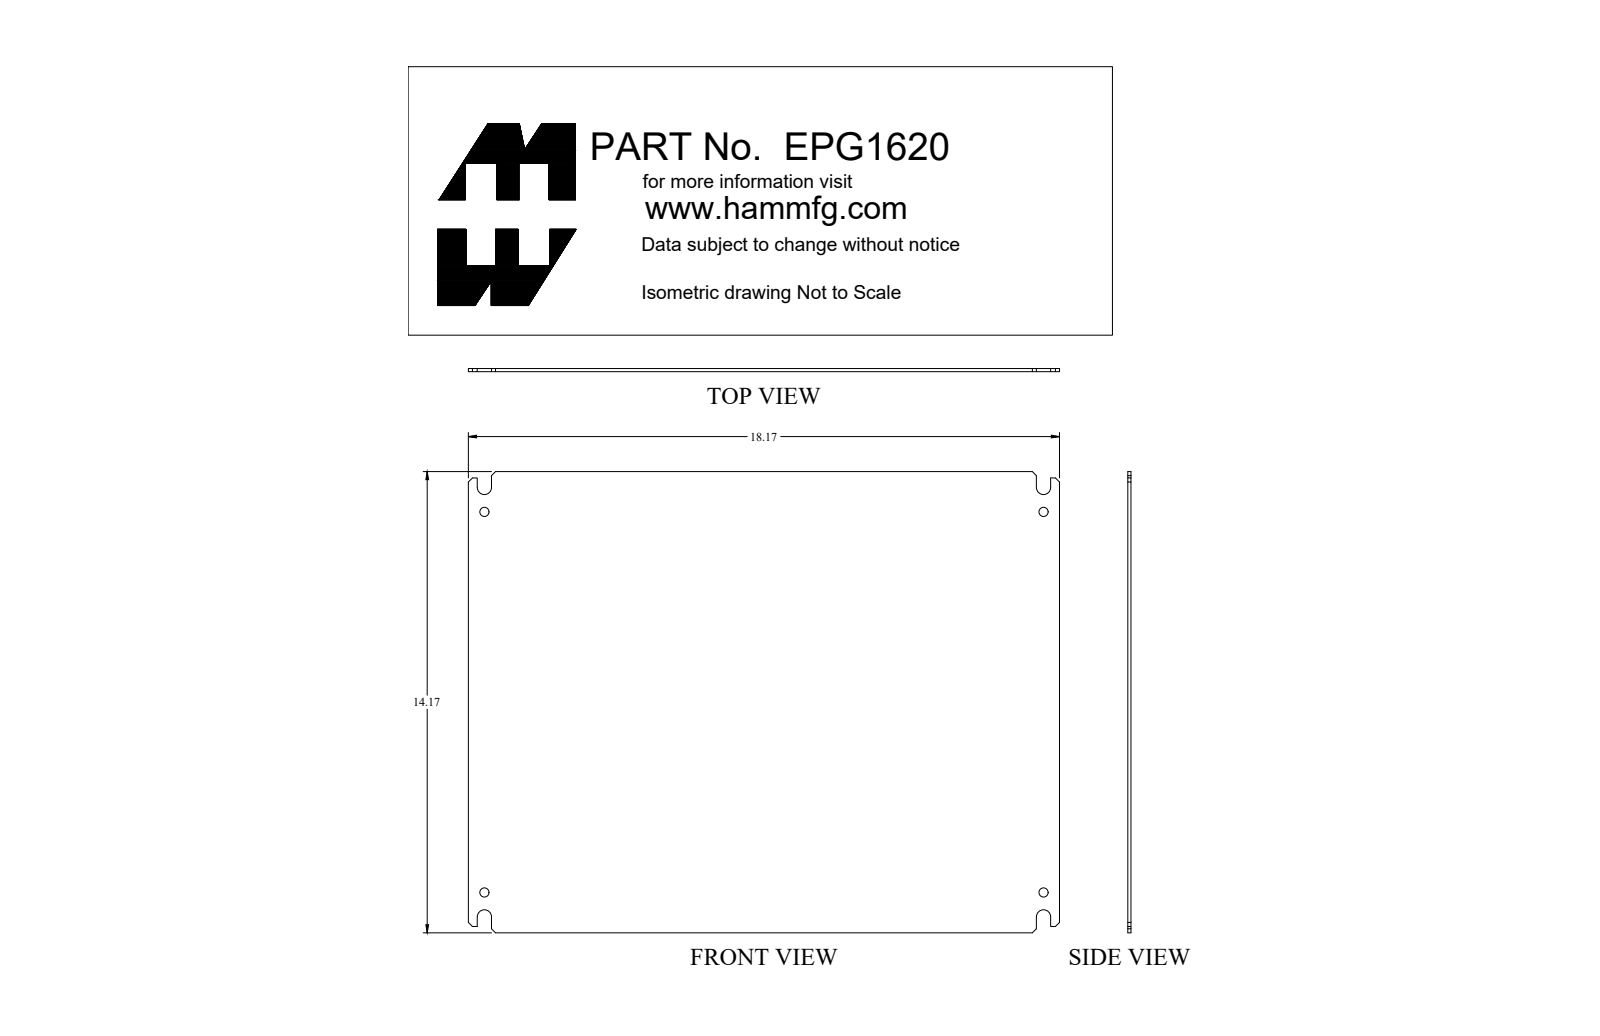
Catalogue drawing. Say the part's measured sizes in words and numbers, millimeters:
The part is named "EPG1620". Its 3-D file was written by "SolidWorks 2018 (AUTOMOTIVE_DESIGN)". It is 1 solid with 40 faces: 26 planar, 14 cylindrical and 0 other. Overall it measures 461.5 by 359.9 by 2.4 millimeters. Its volume is 398 200 cubic millimeters and its surface area 334 400 square millimeters. Round holes: 4 of diameter 7.1. Partial cylindrical surfaces (rounded edges, fillets, slot ends): 4 of radius 5.6. The main face-to-face distances are 2.4, 359.9, 461.5, 18, 443.5, 6.9, 454.6, 11.1, 436.6, 425.5. The hole center spacings are 296.9, 436.6, 528.
